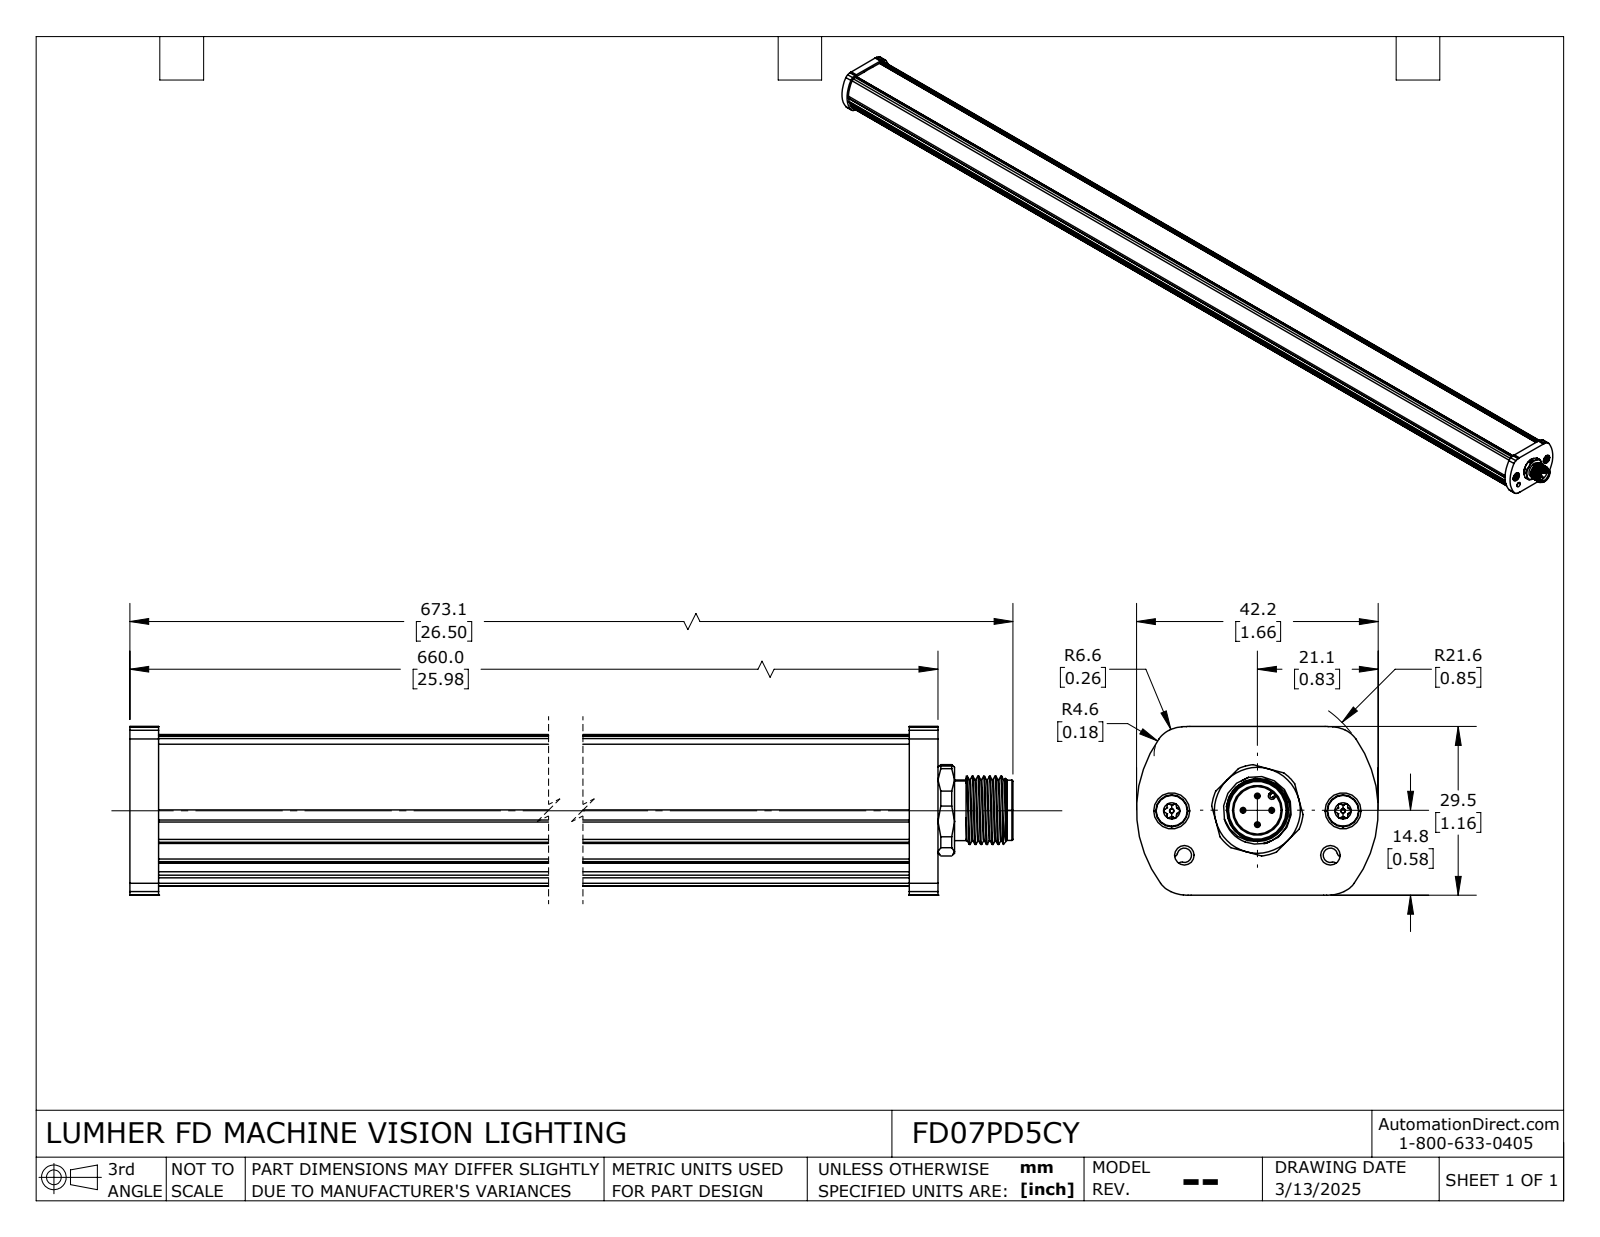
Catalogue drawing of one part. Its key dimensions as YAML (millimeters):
part_name: "FD07PD5CY"
step_written_by: "SolidWorks 2024 (AUTOMOTIVE_DESIGN)"
units: millimeters
bodies: {solids: 1, faces: 662, planar: 97, cylindrical: 383, other: 182}
overall_size: [673.1, 42.21, 29.45]
volume: 559442
surface_area: 135607
round_holes:
  - {diameter: 1.45, count: 4}
  - {diameter: 3.4, count: 4}
  - {diameter: 8.3, count: 1}
  - {diameter: 9, count: 1}
  - {diameter: 9.4, count: 1}
round_bosses_or_shafts:
  - {diameter: 1.4, count: 4}
  - {diameter: 1, count: 4}
  - {diameter: 5.6, count: 2}
  - {diameter: 3, count: 2}
  - {diameter: 0.8, count: 2}
  - {diameter: 11.9, count: 1}
  - {diameter: 10.6, count: 1}
  - {diameter: 10.5, count: 1}
partial_cylinders:
  - {radius: 0.57, count: 24}
  - {radius: 0.25, count: 12}
  - {radius: 0.8, count: 12}
  - {radius: 3, count: 10}
  - {radius: 0.3, count: 4}
  - {radius: 1.25, count: 4}
  - {radius: 3.1, count: 4}
  - {radius: 4.6, count: 4}
face_to_face_distances: [2.5, 5, 7.5, 10, 12.5, 4, 15, 17.5, 2, 3]
hole_center_spacings: [2.5, 3.54, 5, 8.06, 12.91, 13.83, 14.92, 14.95]
